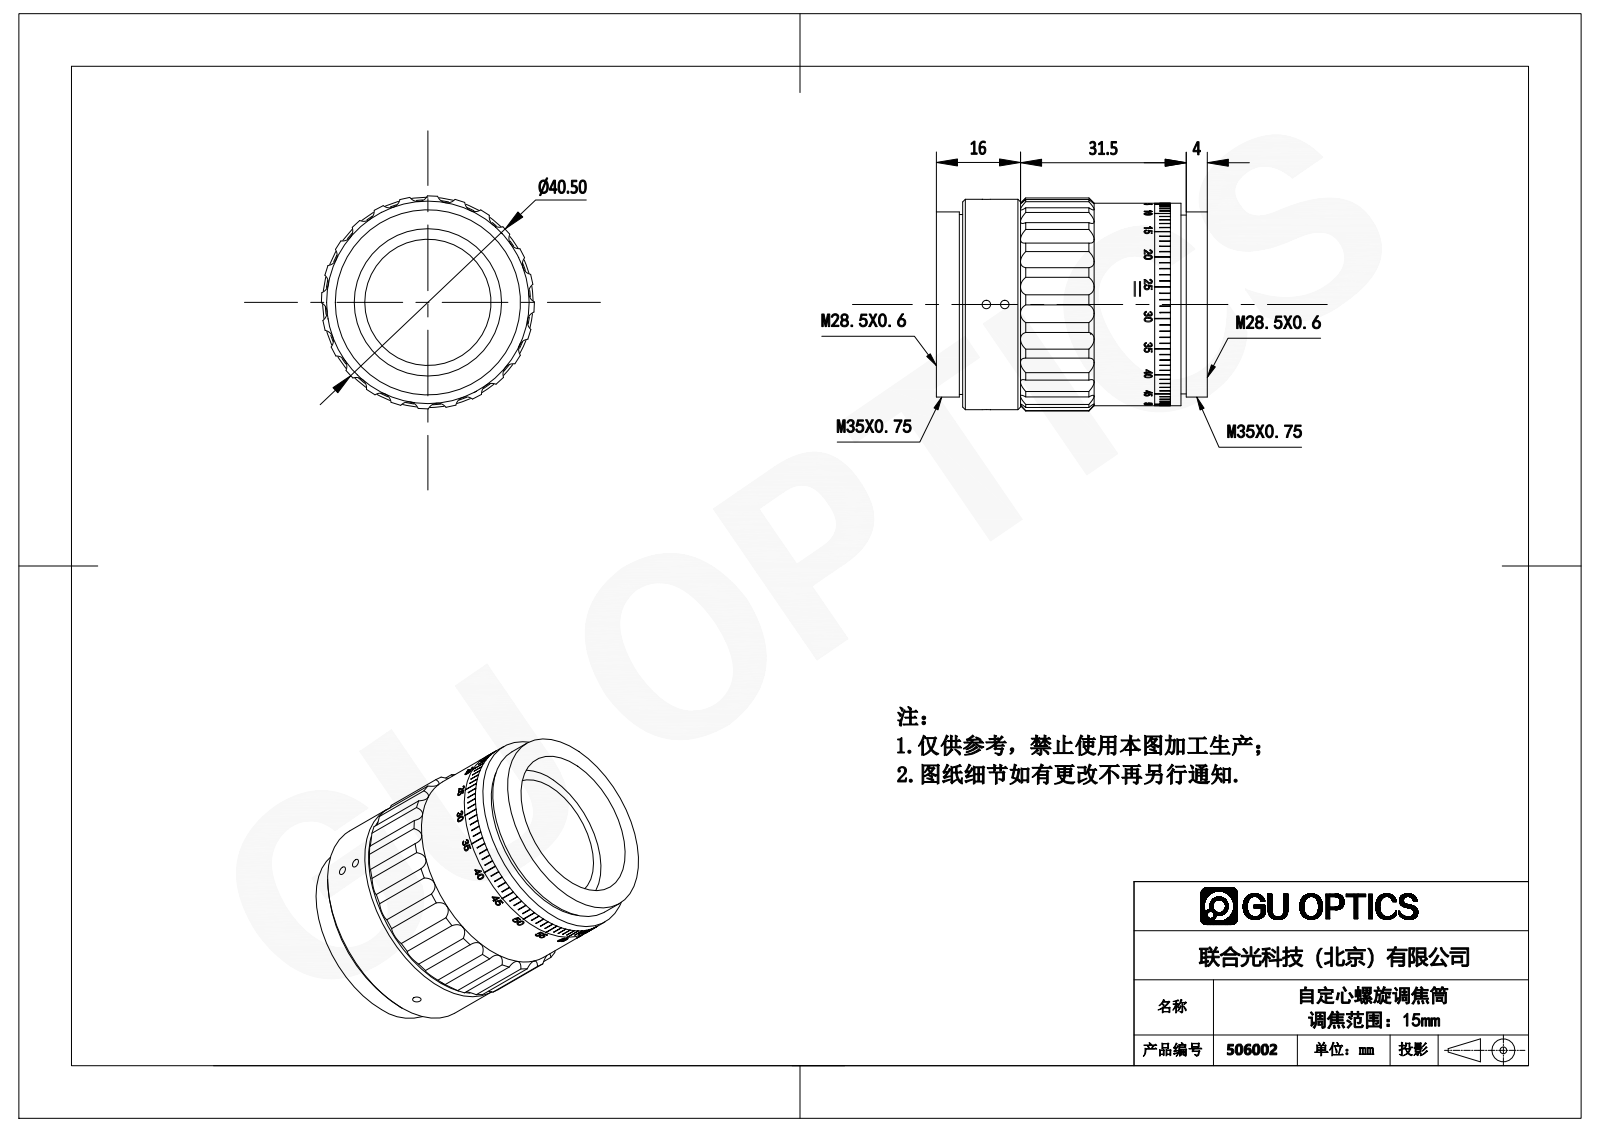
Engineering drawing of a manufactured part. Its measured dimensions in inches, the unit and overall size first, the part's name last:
Units: inches
Overall size (bounding box): 2.028 × 1.594 × 1.594
Round holes (diameter × count): ⌀0.063 ×5, ⌀0.083 ×2, ⌀0.945 ×1, ⌀1.102 ×1, ⌀1.181 ×1, ⌀1.201 ×1, ⌀1.209 ×1, ⌀1.327 ×1, ⌀1.417 ×1, ⌀1.445 ×1, ⌀1.457 ×1
Round bosses / shafts (diameter × count): ⌀0.081 ×4, ⌀0.079 ×4, ⌀1.575 ×1, ⌀1.516 ×1, ⌀1.441 ×1, ⌀1.398 ×1, ⌀1.386 ×1, ⌀1.378 ×1
Partial cylindrical surfaces — rounded edges, fillets, slot ends (radius × count): R0.079 ×24, R0.6 ×4, R0.591 ×2, R0.685 ×1, R0.757 ×1, R0.797 ×1
Main face-to-face distances: 0.197, 0.472, 0.079, 0.039, 0.02, 1.831, 0.394, 1.358, 1.378, 1.634
Hole centre spacings: 0.138
Volume: 2.037 in³ · Surface area: 46.06 in²
Bodies: 8 solids, 1559 faces (658 planar, 351 cylindrical, 550 other)
Part name (STEP PRODUCT): 506002
STEP written by: SolidWorks 2016 (AUTOMOTIVE_DESIGN)
